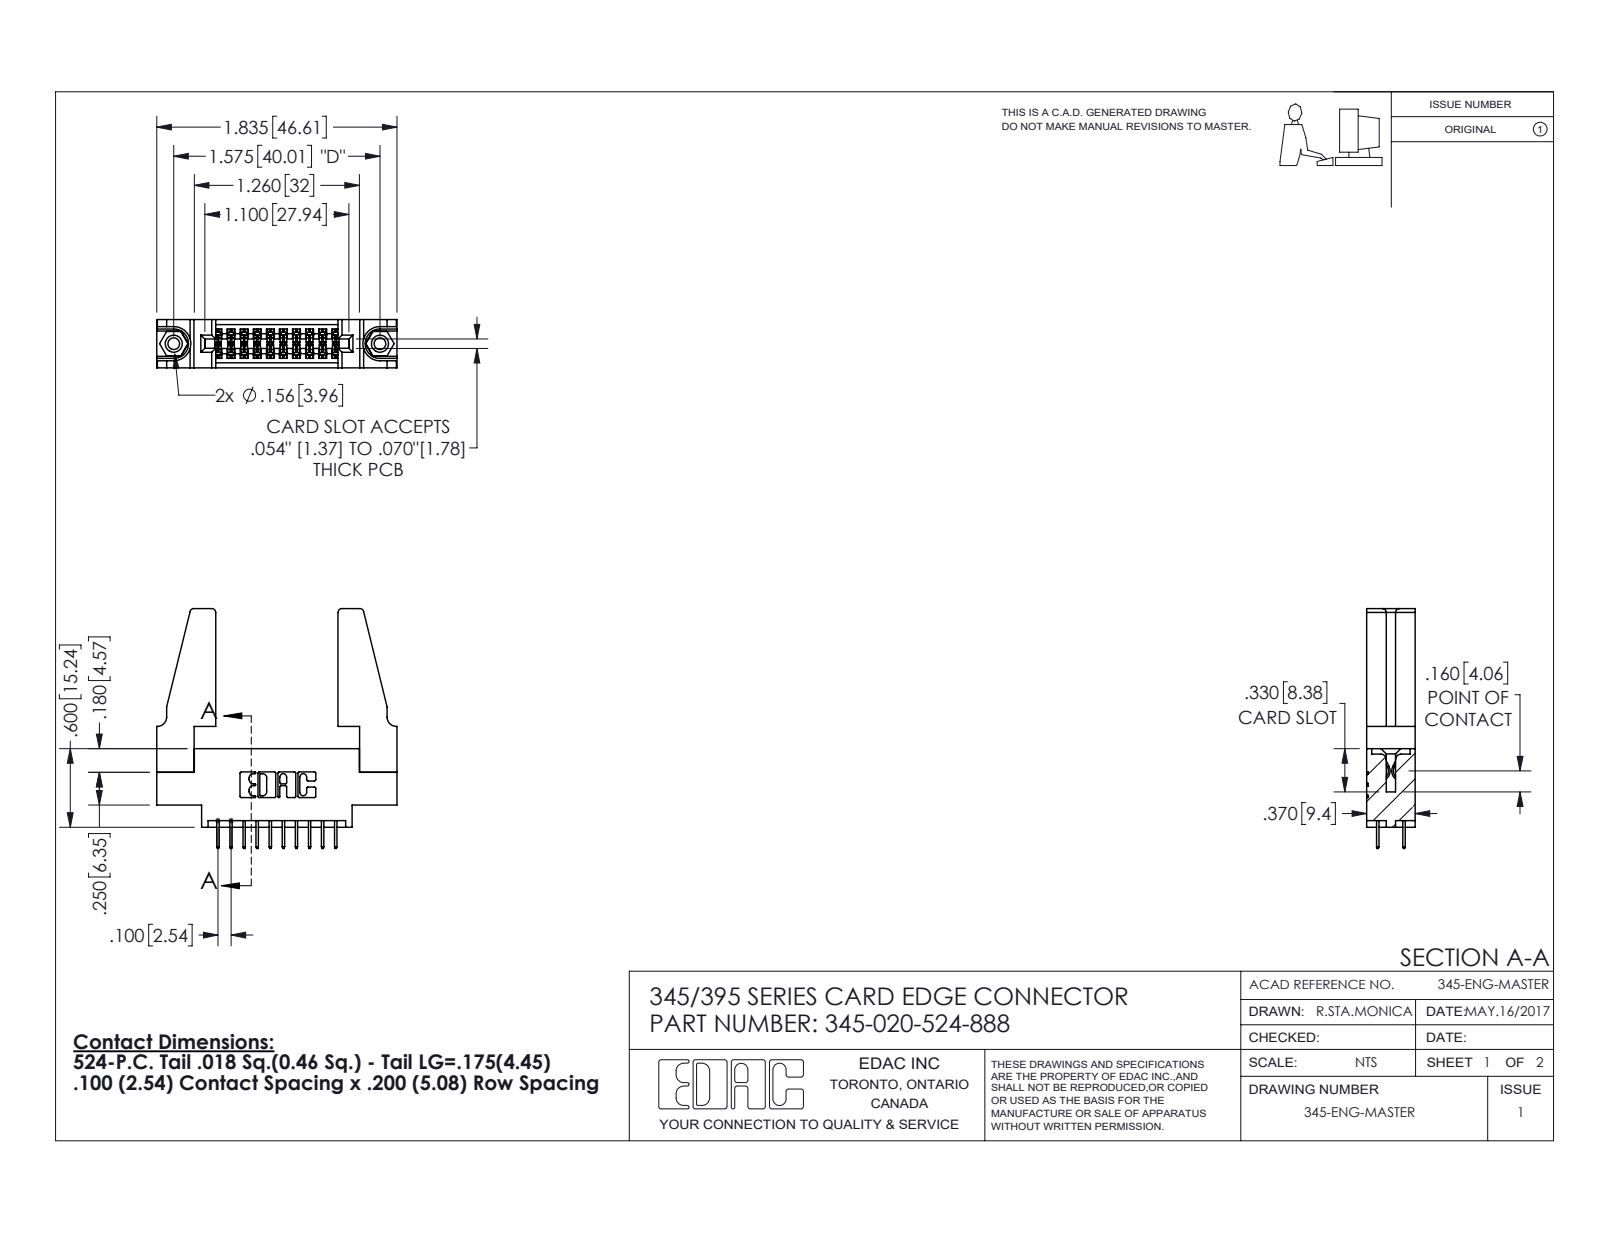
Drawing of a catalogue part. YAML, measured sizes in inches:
part_name: "345-292-001_345-293-124; 345 Part_0.170 Offset - 0.156 Dia-TH; 345-250-001_345-250-001-102; 345-020-524-888 (+1 more)"
step_written_by: "SolidWorks 2016 (CONFIG_CONTROL_DESIGN)"
units: inches
bodies: {solids: 25, faces: 1334, planar: 936, cylindrical: 382, other: 16}
overall_size: [1.836, 1.832, 0.37]
volume: 0.448
surface_area: 13.35
round_holes:
  - {diameter: 0.089, count: 2}
  - {diameter: 0.125, count: 2}
  - {diameter: 0.156, count: 2}
  - {diameter: 0.064, count: 1}
round_bosses_or_shafts:
  - {diameter: 0.155, count: 2}
partial_cylinders:
  - {radius: 0.006, count: 30}
  - {radius: 0.01, count: 22}
  - {radius: 0.03, count: 8}
  - {radius: 0.007, count: 6}
  - {radius: 0.031, count: 6}
  - {radius: 0.026, count: 3}
  - {radius: 0.014, count: 2}
  - {radius: 0.019, count: 2}
face_to_face_distances: [0.37, 0.072, 0.298, 0.2, 0.225, 0.098, 0.272, 0.025, 0.148, 0.15]
hole_center_spacings: [0.27, 1.344, 1.575]
